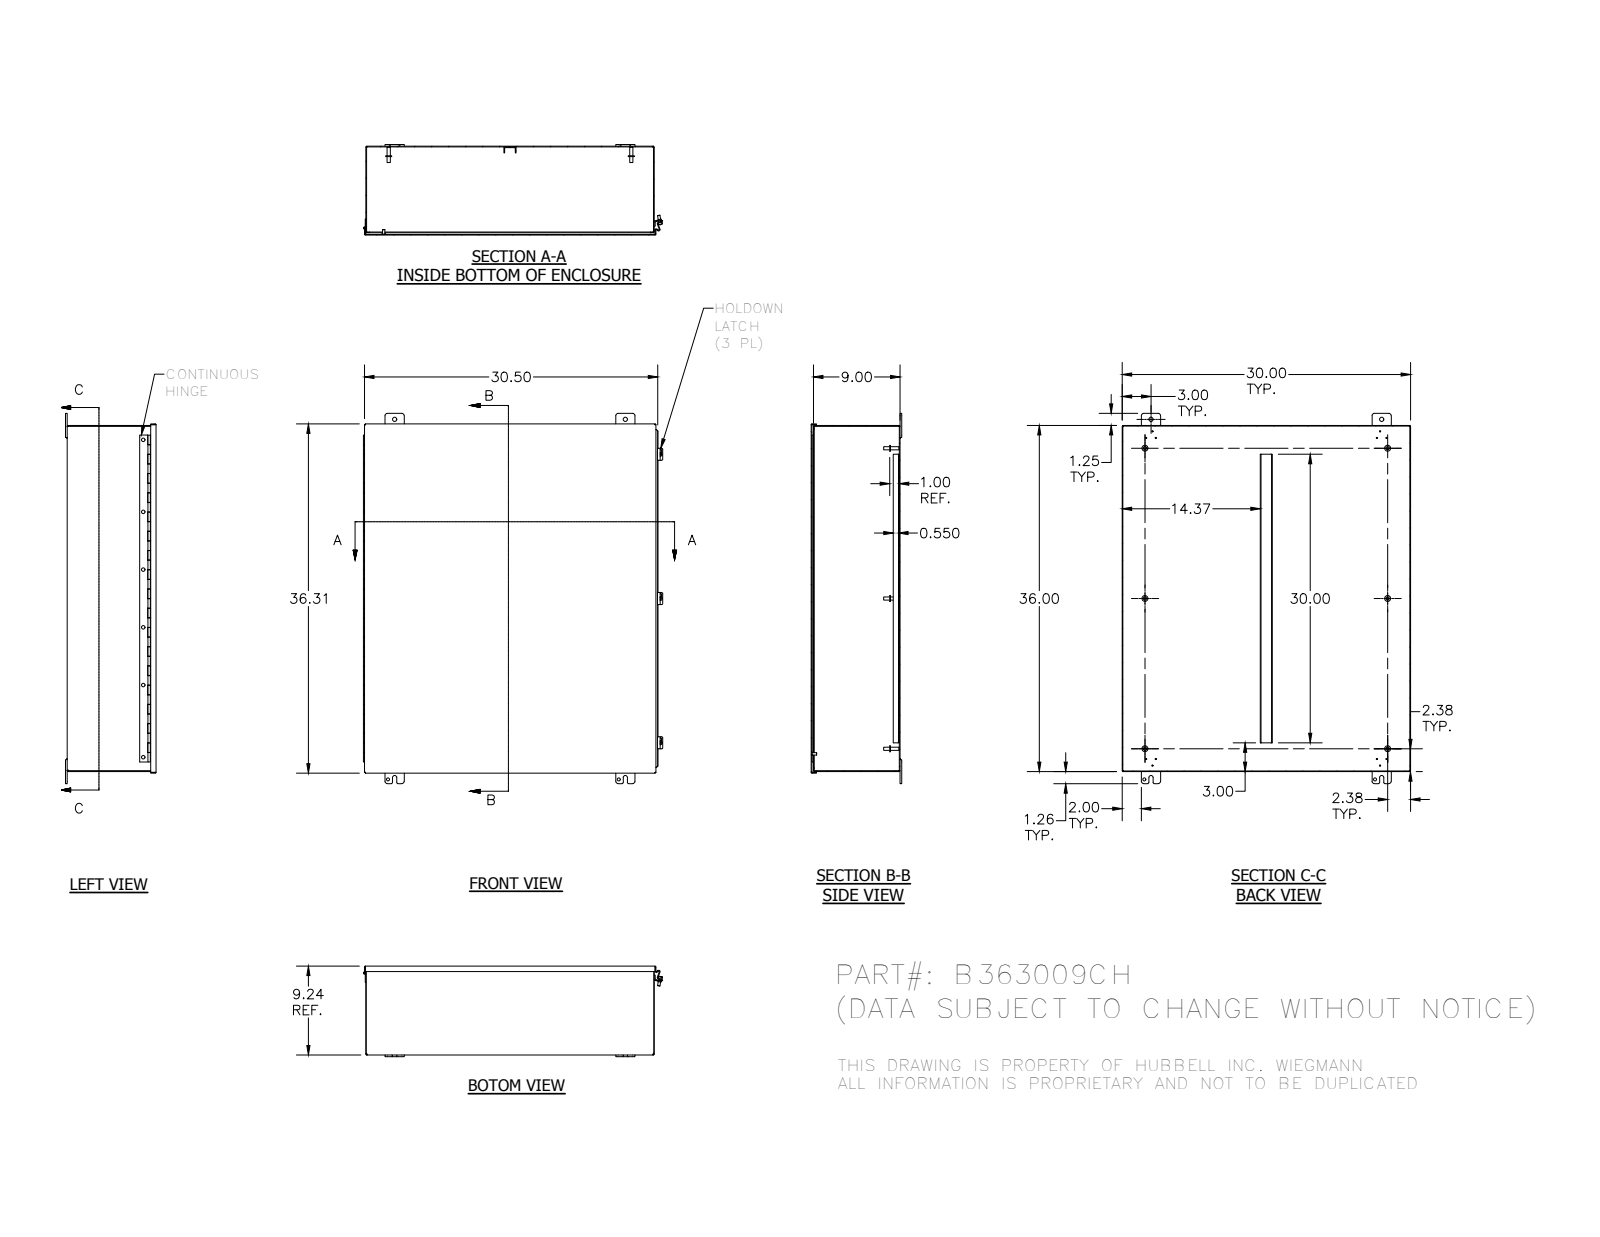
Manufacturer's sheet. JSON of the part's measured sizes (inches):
{"part_name": "B363009CH; B363009CHBKP; B3630CHLID; H6010103 (+8 more)", "step_written_by": "Autodesk Inventor 2012 (AUTOMOTIVE_DESIGN)", "units": "inches", "bodies": {"solids": 26, "faces": 852, "planar": 529, "cylindrical": 245, "other": 78}, "overall_size": [38.505, 31.136, 9.423], "volume_in3": 270.7, "surface_area_in2": 7320, "round_holes": [[0.11, 6], [0.375, 6], [0.313, 4], [0.438, 4], [0.196, 3], [0.125, 1], [0.125, 1]], "round_bosses_or_shafts": [[0.625, 6], [0.33, 6], [0.25, 5], [0.41, 3], [0.344, 3], [0.337, 1], [0.12, 1]], "partial_cylinders_radius": [[0.125, 20], [0.25, 16], [0.063, 12], [0.031, 8], [0.07, 8], [0.105, 8], [0.063, 7], [0.133, 6]], "face_to_face_distances": [0.074, 9.169, 9.095, 9.243, 29.926, 35.926, 30, 29.852, 35.852, 36], "hole_center_spacings": [15, 24, 0.75, 1.593, 6, 36.005, 43.271, 1.134]}
